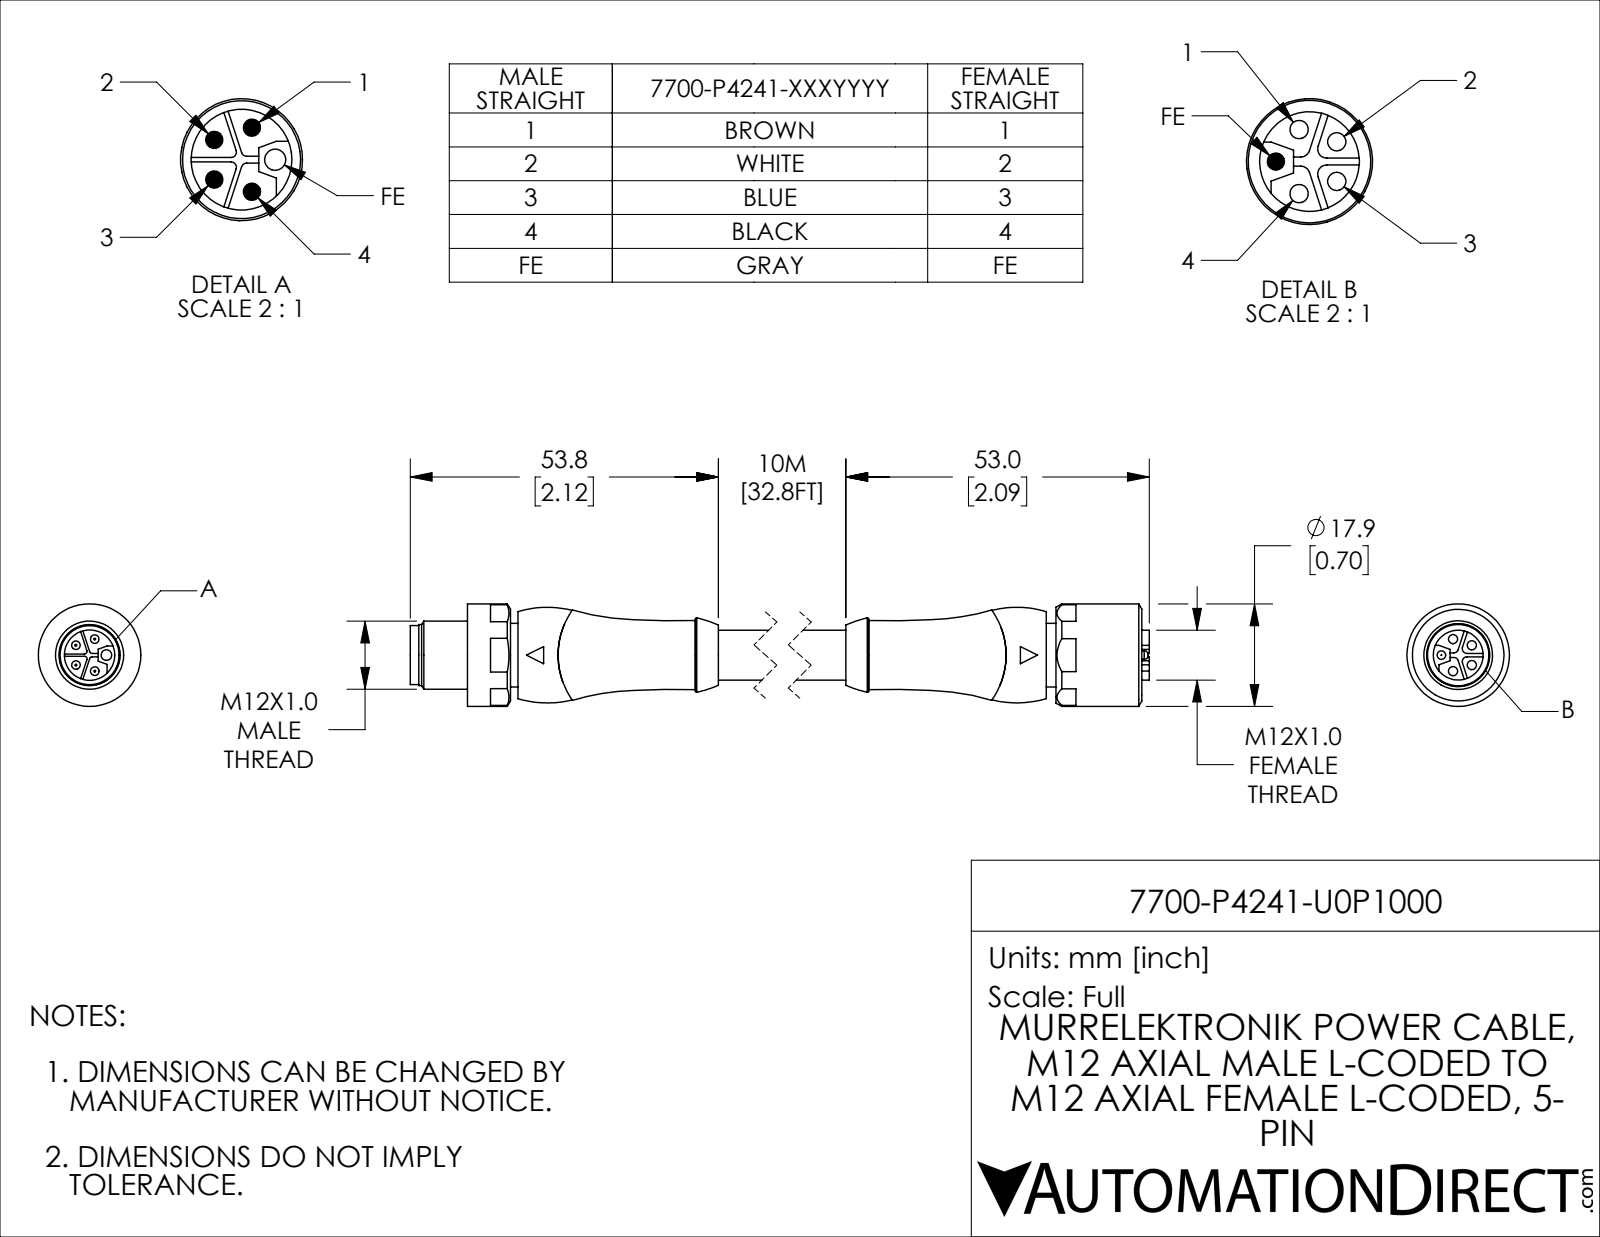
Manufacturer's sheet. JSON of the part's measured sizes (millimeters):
{"part_name": "7700-P4241-U0P1000_2; 7700-P4241-U0P1000_1; 7700-P4241-U0P1000", "step_written_by": "SolidWorks 2021 (CONFIG_CONTROL_DESIGN)", "units": "millimeters", "bodies": {"solids": 3, "faces": 214, "planar": 98, "cylindrical": 62, "other": 54}, "overall_size": [136.8, 17.9, 17.9], "volume_mm3": 17860, "surface_area_mm2": 9316, "round_holes": [[1.6, 4], [1.9, 1], [8.8, 1], [11, 1], [13, 1]], "round_bosses_or_shafts": [[1.5, 5], [17.9, 1], [13, 1], [11.9, 1], [11.1, 1], [10.6, 1], [10.3, 1], [8.7, 1]], "partial_cylinders_radius": [[0.5, 4], [0.8, 4]], "face_to_face_distances": [108.8, 1.7, 8.8, 16.9, 1.3, 7.5, 5.8, 125.5, 16.7, 110.5], "hole_center_spacings": [2.9, 3.5, 5.6, 5.6]}
